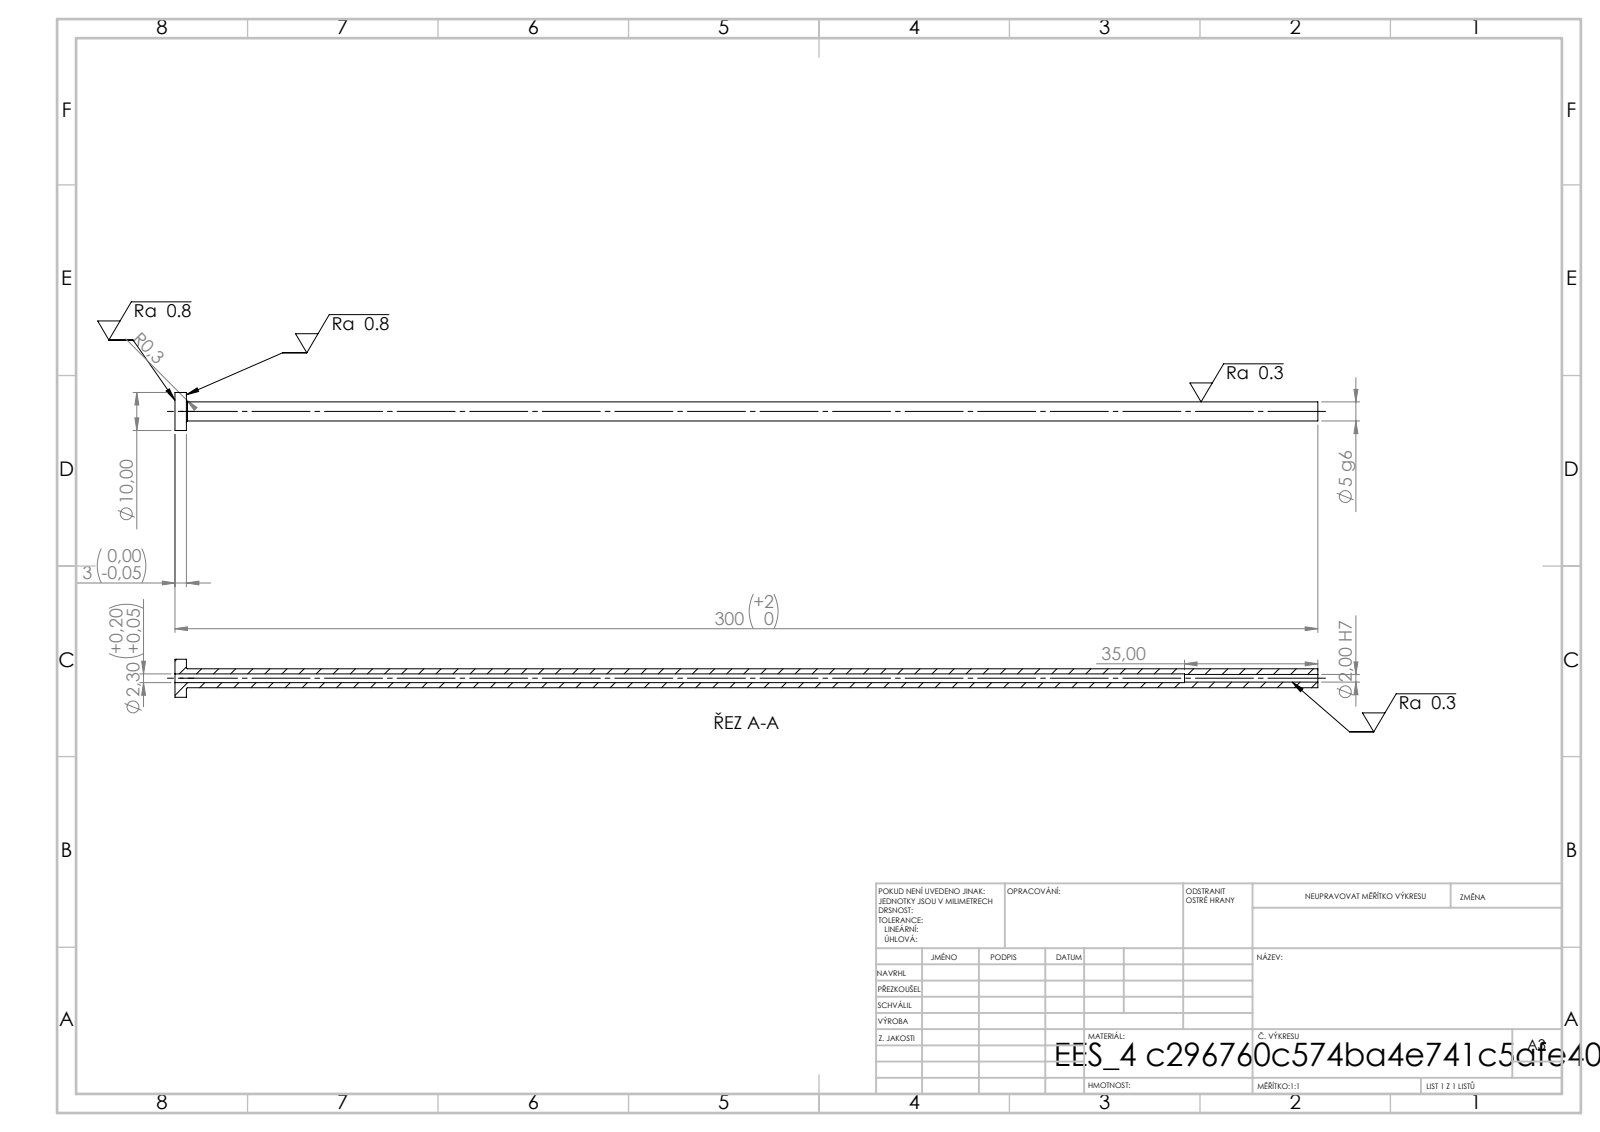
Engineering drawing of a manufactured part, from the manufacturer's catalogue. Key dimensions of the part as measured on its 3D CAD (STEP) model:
STEP written by: SolidWorks 2019 (CONFIG_CONTROL_DESIGN)
Units: millimetres
Bodies: 1 solid, 14 faces (4 planar, 8 cylindrical, 2 other)
Overall size (bounding box): 300 × 10 × 10
Volume: 4 857 mm³ · Surface area: 7 043 mm²
Round holes (diameter × count): ⌀2 ×1, ⌀2.3 ×1
Round bosses / shafts (diameter × count): ⌀10 ×1, ⌀5 ×1
Main face-to-face distances: 3, 300, 297, 265, 262, 35
